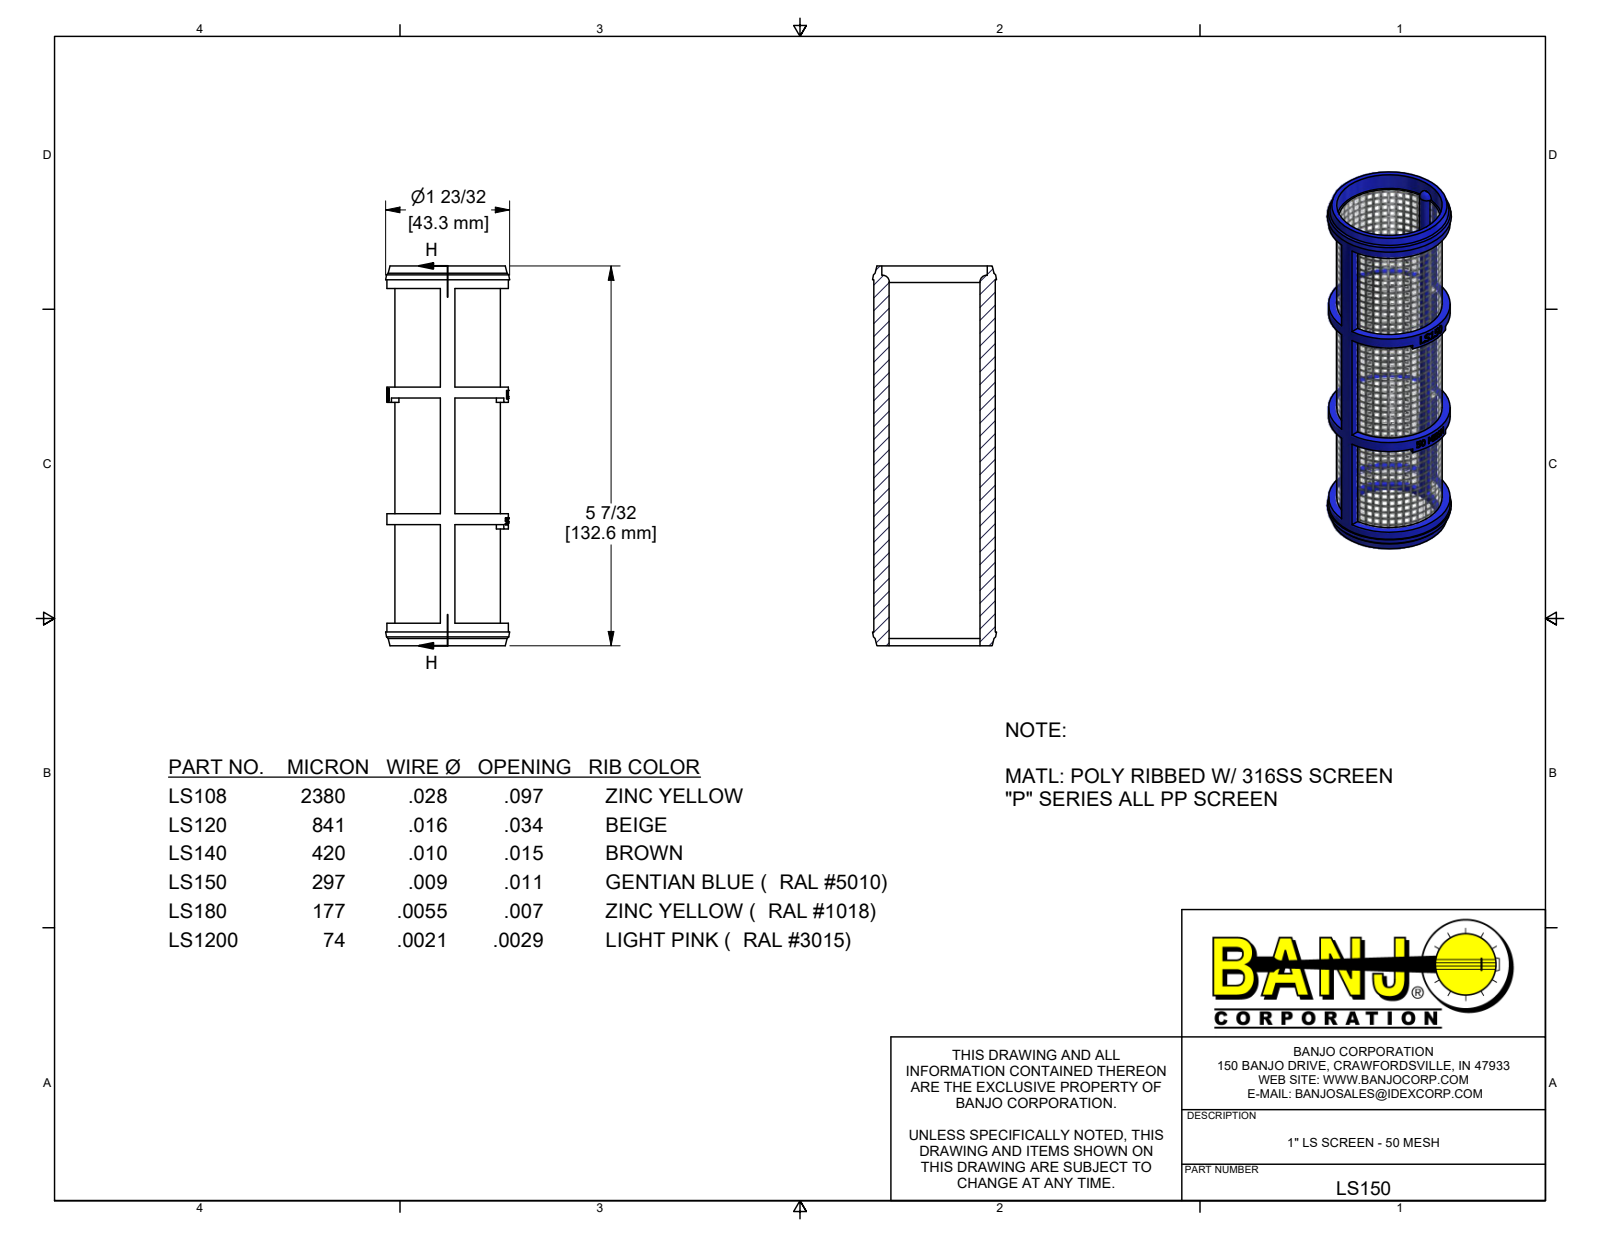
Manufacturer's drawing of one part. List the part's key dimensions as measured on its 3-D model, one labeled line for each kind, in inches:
Part name (STEP PRODUCT): LS150
STEP written by: Autodesk Inventor 2019 (AUTOMOTIVE_DESIGN)
Units: inches
Bodies: 1 solid, 391 faces (246 planar, 42 cylindrical, 103 other)
Overall size (bounding box): 5.22 × 1.705 × 1.705
Volume: 1.373 in³ · Surface area: 54.95 in²
Round holes (diameter × count): ⌀1.25 ×1, ⌀1.4 ×1
Round bosses / shafts (diameter × count): ⌀1.67 ×1, ⌀1.45 ×1
Partial cylindrical surfaces — rounded edges, fillets, slot ends (radius × count): R0.1 ×2, R0.815 ×1
Main face-to-face distances: 0.2, 1.74, 1.815, 3.555, 0.15, 1.665, 3.405, 0.31, 1.505, 3.245
